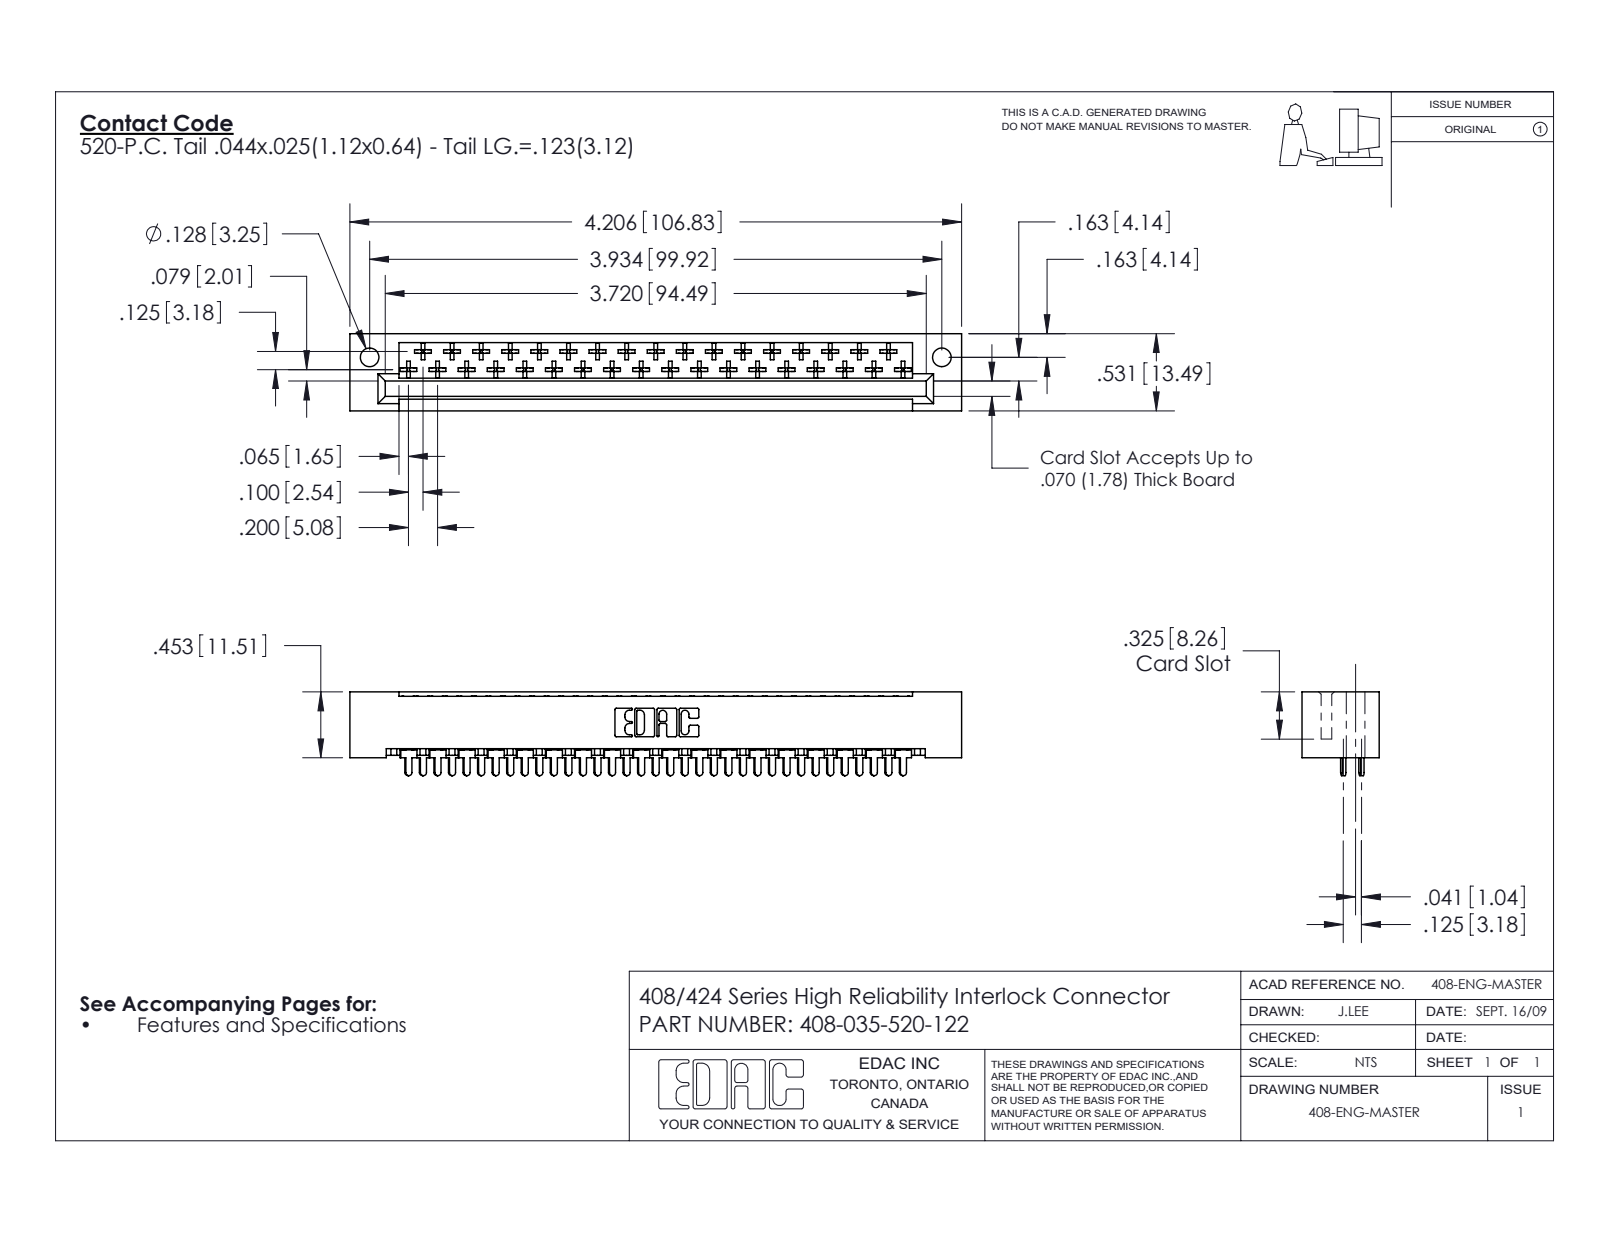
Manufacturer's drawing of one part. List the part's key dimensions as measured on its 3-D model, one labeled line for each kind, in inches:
Part name (STEP PRODUCT): 408 Part_035 - 1; 408-035-520-122; 408-290-001_408-290-120
STEP written by: SolidWorks 2016 (CONFIG_CONTROL_DESIGN)
Units: inches
Bodies: 36 solids, 2052 faces (1549 planar, 363 cylindrical, 140 other)
Overall size (bounding box): 4.206 × 0.576 × 0.531
Volume: 0.711 in³ · Surface area: 22.36 in²
Round holes (diameter × count): ⌀0.128 ×2
Partial cylindrical surfaces — rounded edges, fillets, slot ends (radius × count): R0.01 ×210, R0.02 ×37, R0.022 ×35, R0.01 ×22, R0.007 ×6, R0.031 ×6, R0.026 ×3
Main face-to-face distances: 0.1, 0.296, 0.531, 0.025, 0.125, 0.025, 0.272, 0.235, 0.259, 0.135
Hole centre spacings: 3.934
